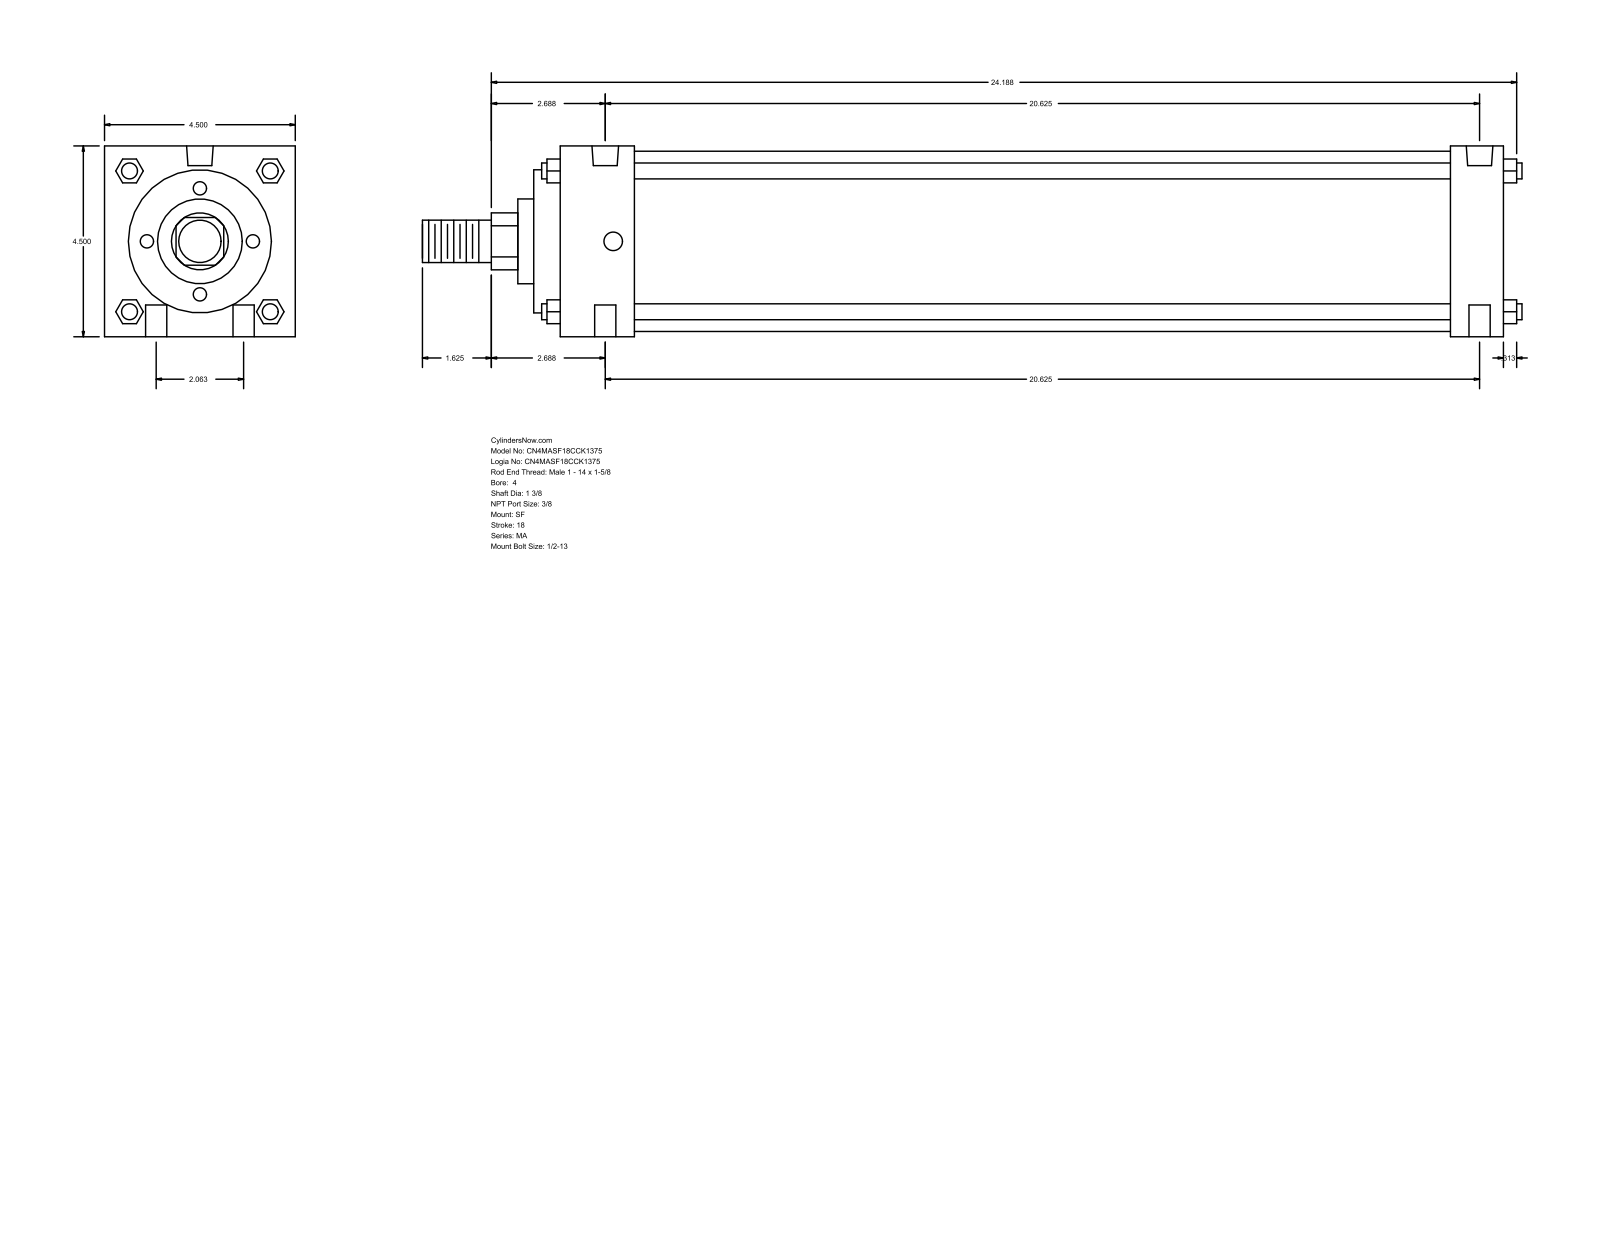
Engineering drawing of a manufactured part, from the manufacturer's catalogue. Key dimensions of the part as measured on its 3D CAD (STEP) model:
Part name (STEP PRODUCT): MA_SF__0400_1.375
STEP written by: GSSL Pune (CONFIG_CONTROL_DESIGN)
Units: millimetres
Bodies: 0 solids, 126 faces (95 planar, 31 cylindrical, 0 other)
Overall size (bounding box): 658.81 × 114.3 × 114.3
Round holes (diameter × count): ⌀12.7 ×4, ⌀11.11 ×2, ⌀15.93 ×2
Round bosses / shafts (diameter × count): ⌀9.53 ×4, ⌀107.95 ×1, ⌀85.72 ×1, ⌀50.8 ×1, ⌀34.92 ×1, ⌀25.4 ×1
Partial cylindrical surfaces — rounded edges, fillets, slot ends (radius × count): R17.06 ×1
Main face-to-face distances: 114.3, 565.15, 581.02, 15.87, 549.27, 533.4, 31.75, 60.32, 44.45, 488.95
Hole centre spacings: 26.19, 524.53, 523.88, 52.38, 526.49, 514.35
